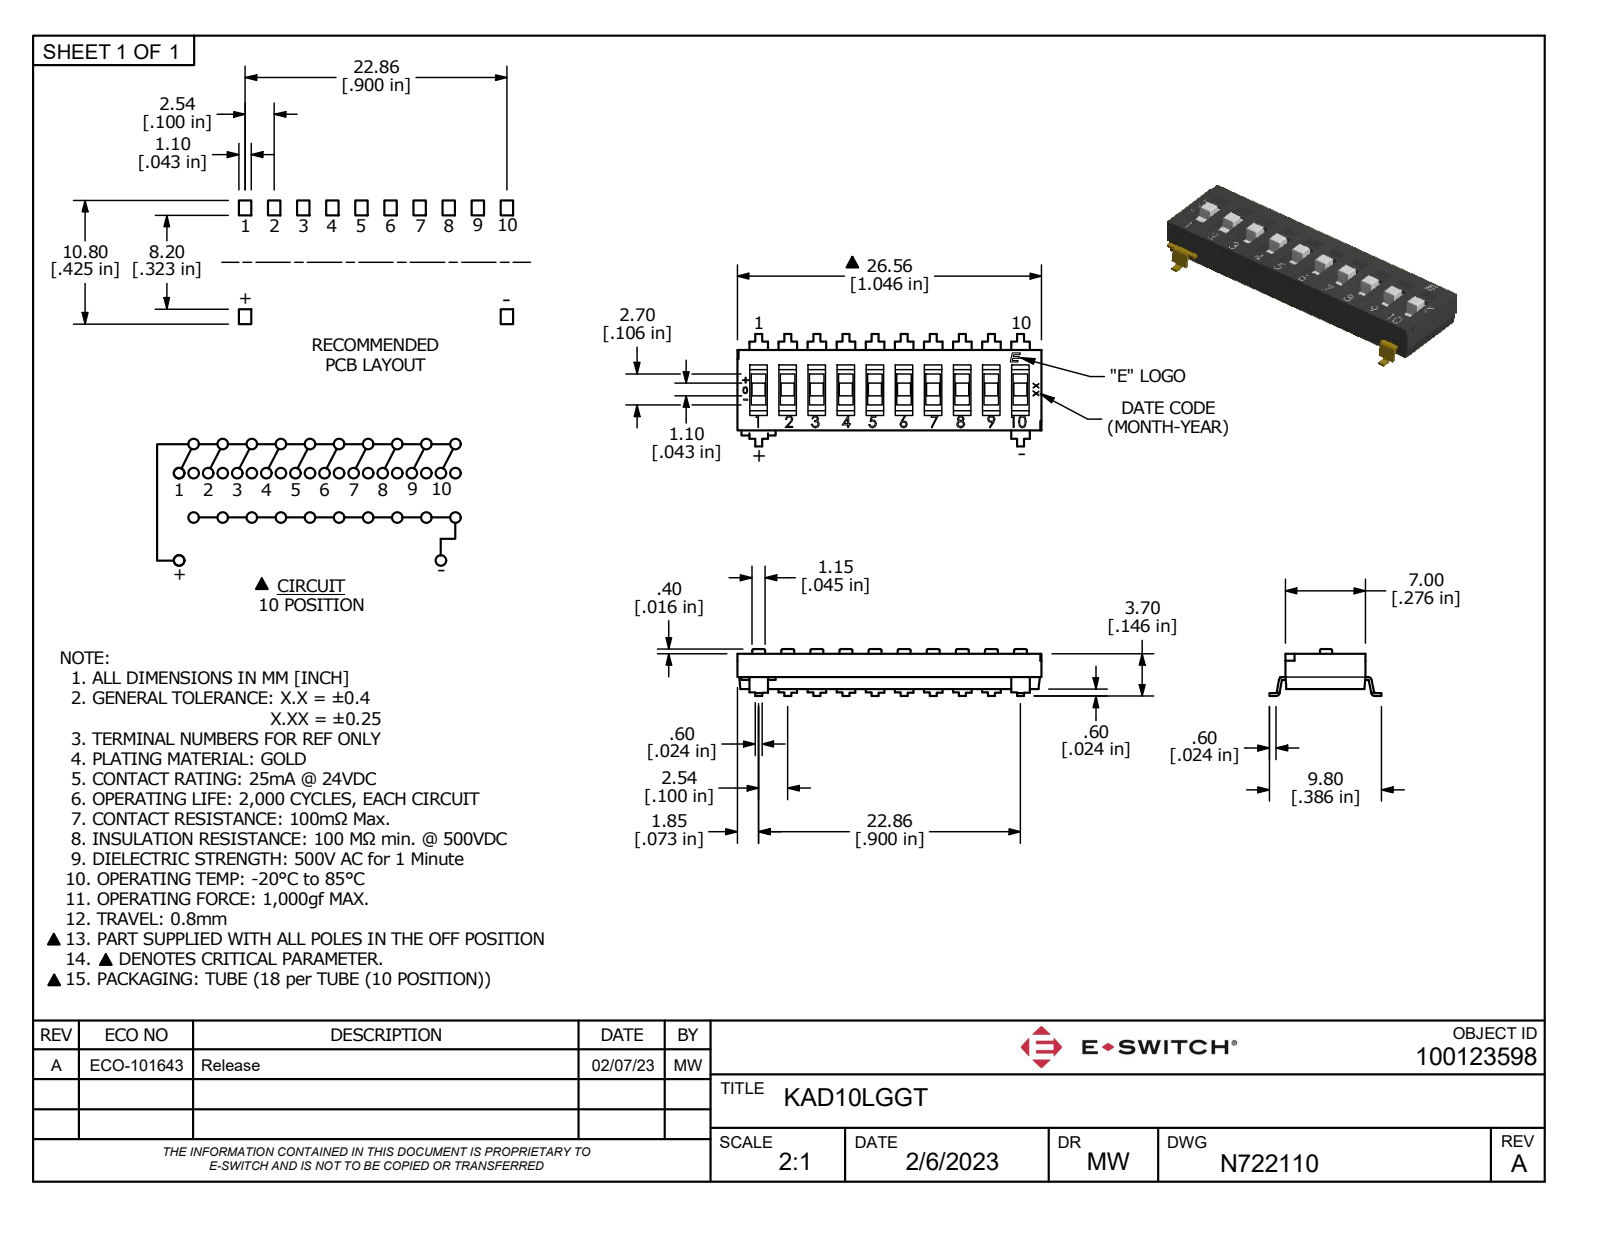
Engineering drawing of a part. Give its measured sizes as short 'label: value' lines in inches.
name: KAD10LGGT
written by: Autodesk Inventor 2022 (AUTOMOTIVE_DESIGN)
unit: in
bodies: 1 solid, 685 faces (508 planar, 88 cylindrical, 89 other)
size: 1.046 × 0.386 × 0.161
volume: 0.034 in³; area: 1.21 in²
rounds: 24× R0.004, 4× R0.012
face distances: 0.122, 0.276, 0.1, 0.2, 0.016, 0.106, 0.3, 0.031, 0.059, 0.033
